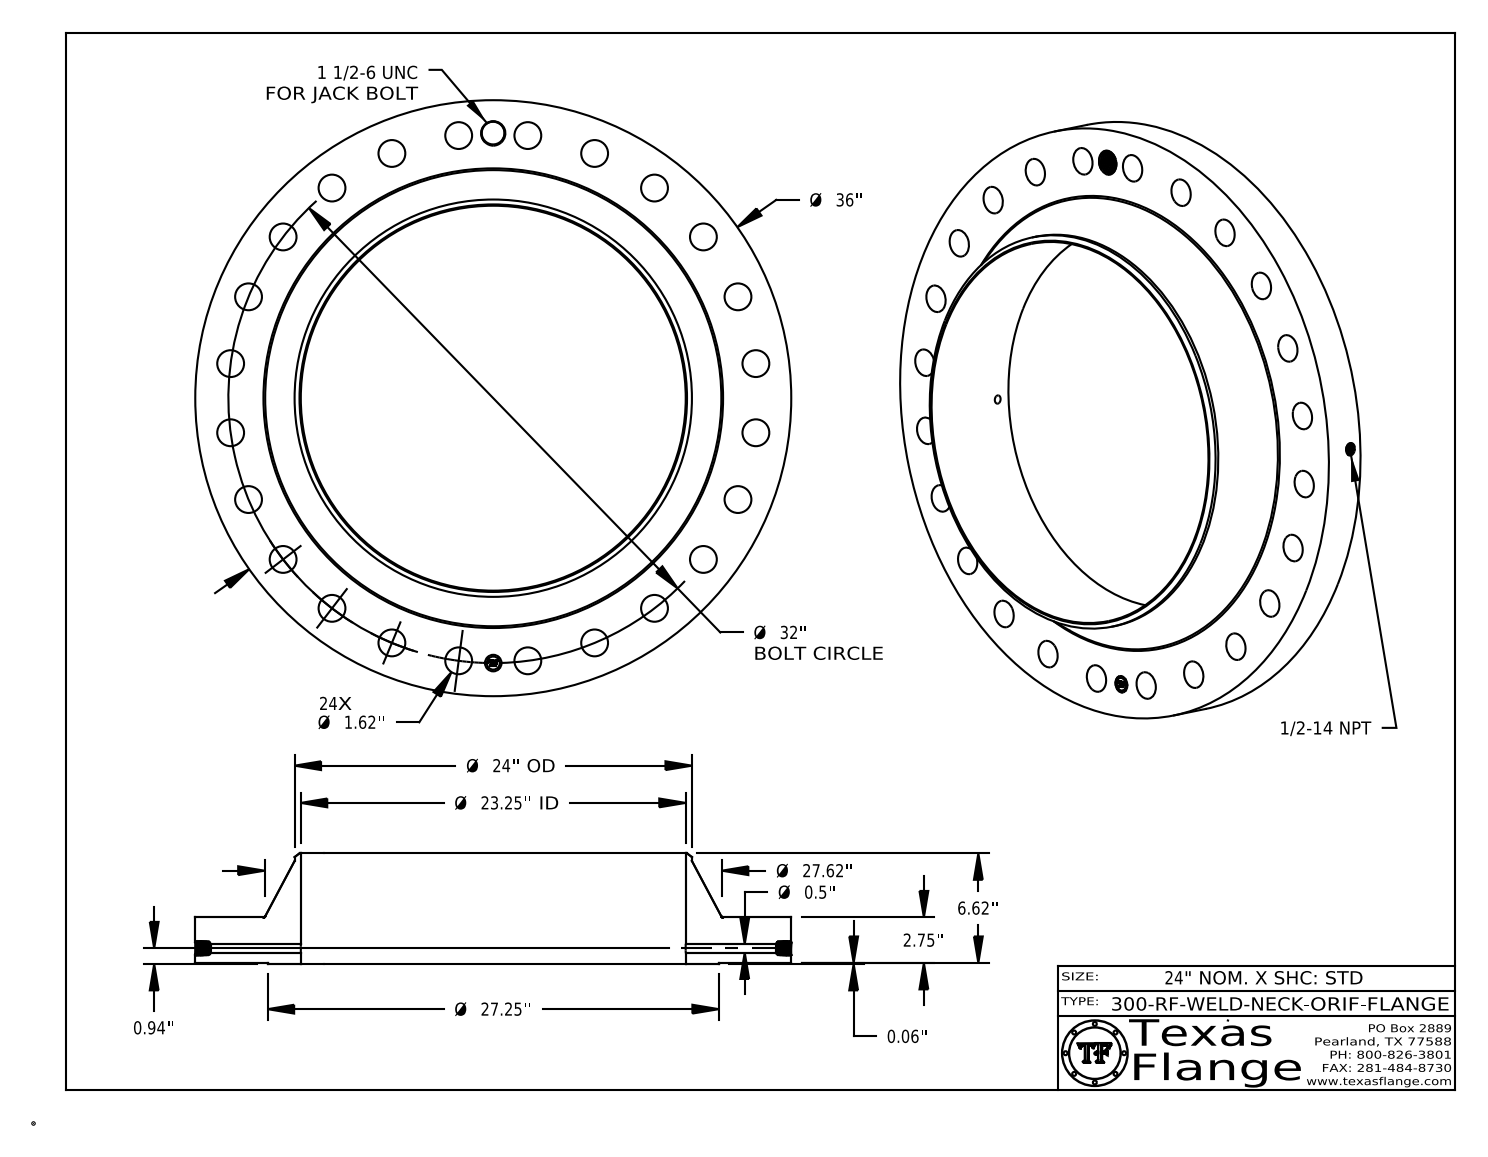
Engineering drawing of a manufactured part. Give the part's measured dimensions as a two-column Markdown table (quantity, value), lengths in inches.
| quantity | value |
| --- | --- |
| part name | 300-RF-WELD-NECK |
| STEP written by | CATIA V5 STEP AP214 (AUTOMOTIVE_DESIGN) |
| units | inches |
| bodies | 1 solid, 810 faces (369 planar, 129 cylindrical, 312 other) |
| overall size | 36 × 36 × 6.68 |
| volume | 1 847 in³ |
| surface area | 2 453 in² |
| round holes (diameter × count) | 1.62 × 24, 0.5 × 1, 0.672 × 1, 1 × 1, 1.344 × 1, 23.25 × 1 |
| round bosses / shafts (diameter × count) | 0.061 × 8, 36 × 1, 27.25 × 1, 24 × 1, 0.788 × 1 |
| main face-to-face distances | 2.75, 0.06, 2.81, 6.68, 6.62, 3.87, 2.795, 2.735, 0.015, 3.885 |
| hole center spacings | 16, 27.713, 30.909, 4.177, 19.48, 31.726, 8.282, 12.246 |
